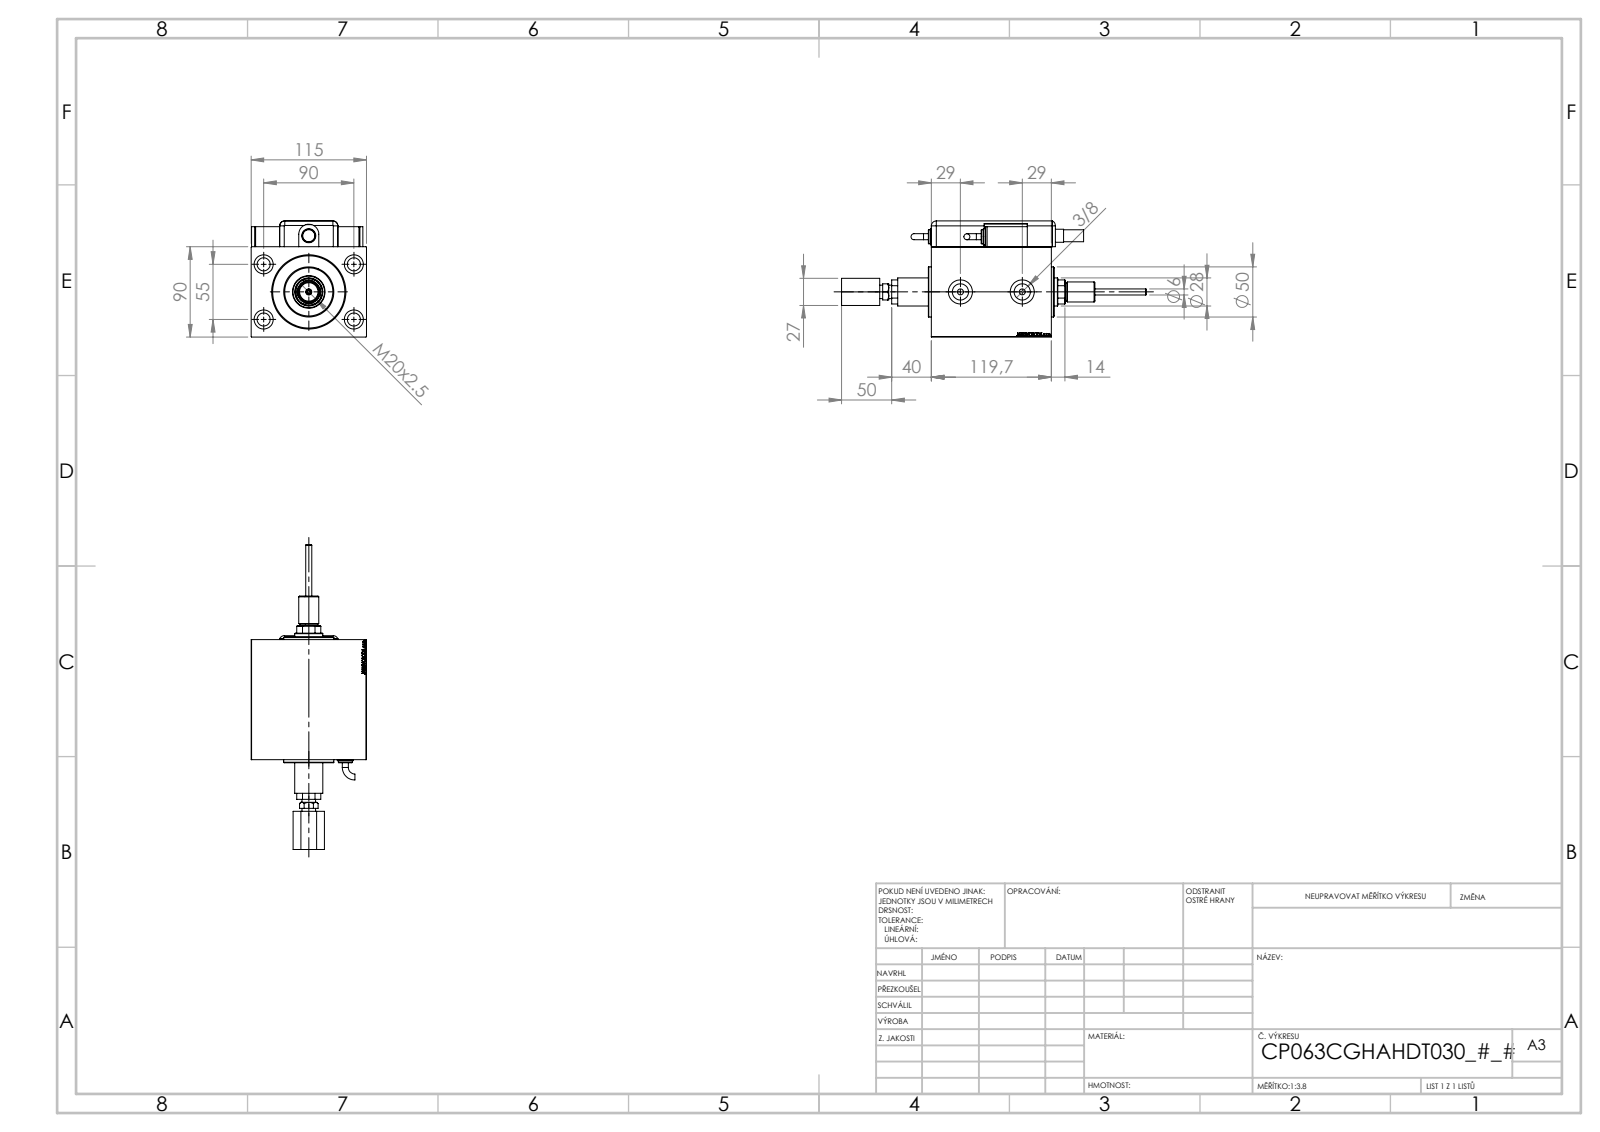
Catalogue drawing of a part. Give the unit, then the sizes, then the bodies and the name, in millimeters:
Units: millimetres
Overall size (bounding box): 303.7 × 115.8 × 115
Round holes (diameter × count): ⌀4 ×4, ⌀13 ×4, ⌀19 ×4, ⌀6 ×3, ⌀8 ×2, ⌀9.73 ×2, ⌀15 ×2, ⌀16.17 ×2, ⌀24 ×2, ⌀3 ×1, ⌀14 ×1, ⌀18.5 ×1
Round bosses / shafts (diameter × count): ⌀20 ×3, ⌀16 ×2, ⌀14 ×2, ⌀6 ×2, ⌀50 ×1, ⌀18 ×1, ⌀13.47 ×1, ⌀13 ×1
Partial cylindrical surfaces — rounded edges, fillets, slot ends (radius × count): R5 ×9, R10 ×1, R13.5 ×1
Main face-to-face distances: 90, 3, 115, 119.7, 1, 17.5, 102.2, 30, 25.8, 115.8
Hole centre spacings: 52.74, 53.27, 55, 90, 94.85, 105.48, 20, 22.18
Volume: 1 279 000 mm³ · Surface area: 228 089 mm²
Bodies: 11 solids, 1306 faces (626 planar, 149 cylindrical, 531 other)
Part name (STEP PRODUCT): SWITCH_Q_FRONT_BACK; V450DCP_C_Body; KRYT; V450DCP_B_RodCooling_ACCESSORIES (+6 more)
STEP written by: SolidWorks 2019 (CONFIG_CONTROL_DESIGN)
